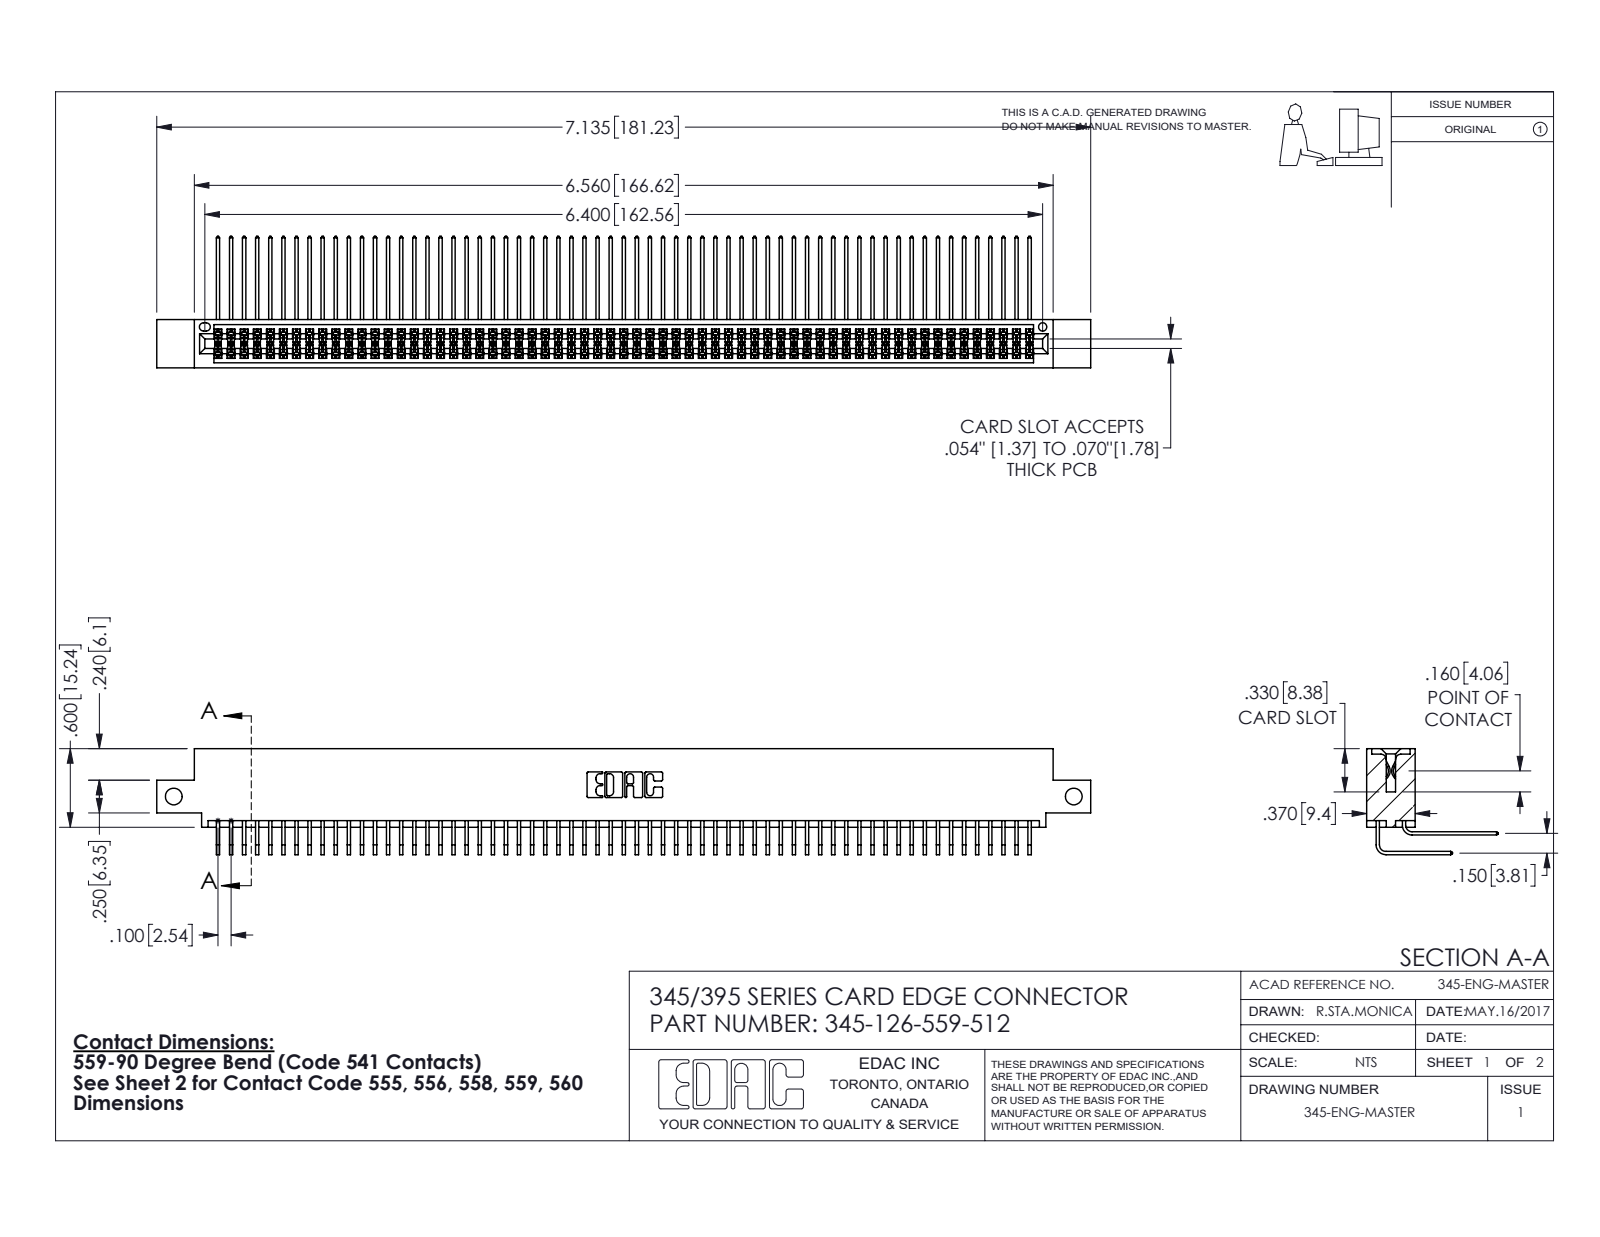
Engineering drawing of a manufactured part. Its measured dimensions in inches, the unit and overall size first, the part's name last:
Units: inches
Overall size (bounding box): 7.135 × 1.005 × 0.809
Round holes (diameter × count): ⌀0.128 ×2, ⌀0.064 ×1
Partial cylindrical surfaces — rounded edges, fillets, slot ends (radius × count): R0.006 ×251, R0.01 ×22, R0.007 ×6, R0.031 ×6, R0.026 ×3, R0.014 ×2, R0.019 ×2, R0.022 ×2
Main face-to-face distances: 0.072, 0.298, 0.2, 0.37, 0.098, 0.272, 0.025, 0.225, 0.175, 0.15
Hole centre spacings: 6.875
Volume: 1.121 in³ · Surface area: 47.94 in²
Bodies: 127 solids, 6682 faces (4494 planar, 2188 cylindrical, 0 other)
Part name (STEP PRODUCT): 345-292-001_558 559 Tail - 1; 345-126-559-512; 345 Part_0.110 Offset - Side Mount; 345-292-001_559 Tail - 2
STEP written by: SolidWorks 2016 (CONFIG_CONTROL_DESIGN)
